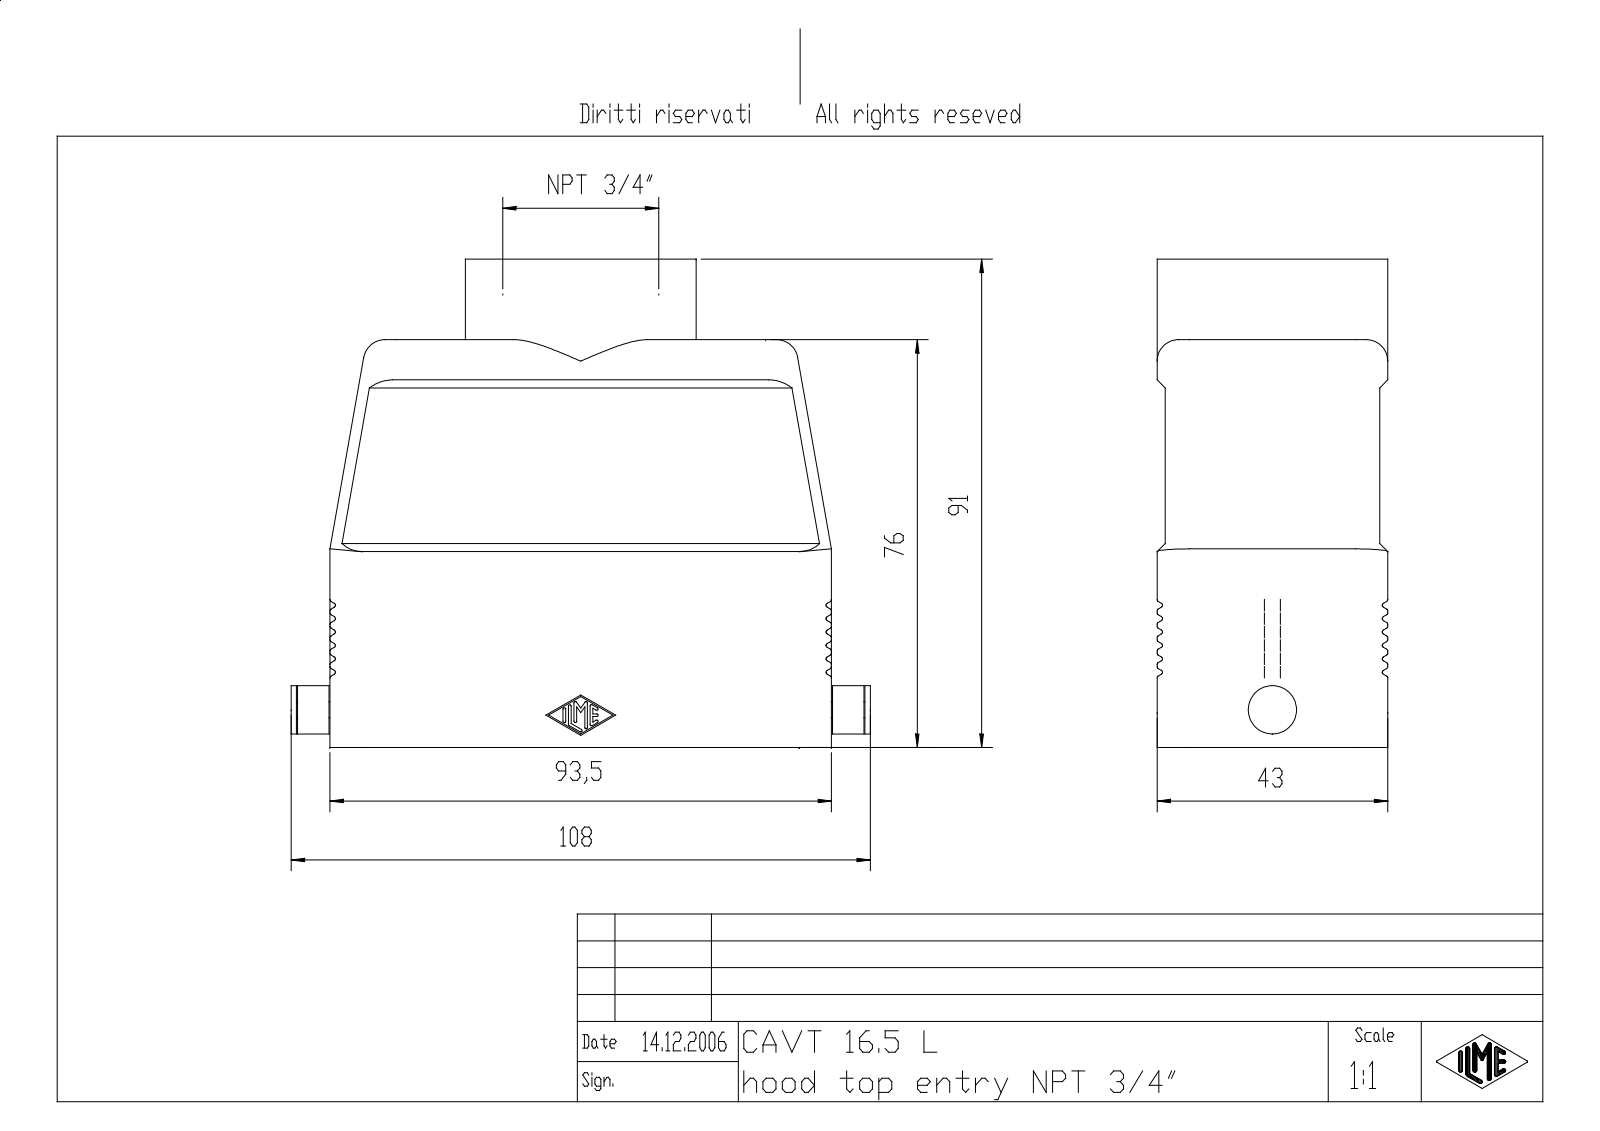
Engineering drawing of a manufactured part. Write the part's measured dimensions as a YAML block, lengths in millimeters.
part_name: "MSBO14095"
step_written_by: "Creo Elements/Direct Modeling 18.0B 02-Dec-2011 (C) Parametric Technology GmbH (AUTOMOTIVE_DESIGN)"
units: millimeters
bodies: {solids: 1, faces: 650, planar: 230, cylindrical: 262, other: 158}
overall_size: [108, 91, 43]
volume: 82793
surface_area: 49142
round_holes:
  - {diameter: 2.46, count: 4}
  - {diameter: 3.1, count: 4}
round_bosses_or_shafts:
  - {diameter: 43, count: 1}
  - {diameter: 9, count: 1}
  - {diameter: 3, count: 1}
partial_cylinders:
  - {radius: 0.4, count: 96}
  - {radius: 0.25, count: 14}
  - {radius: 6, count: 8}
  - {radius: 1.5, count: 4}
  - {radius: 3, count: 4}
  - {radius: 4, count: 4}
  - {radius: 5, count: 4}
face_to_face_distances: [1.5, 3, 40, 37, 38.5, 41.5, 43, 8.25, 79.25, 11.25]
hole_center_spacings: [27, 77.5, 82.07]
